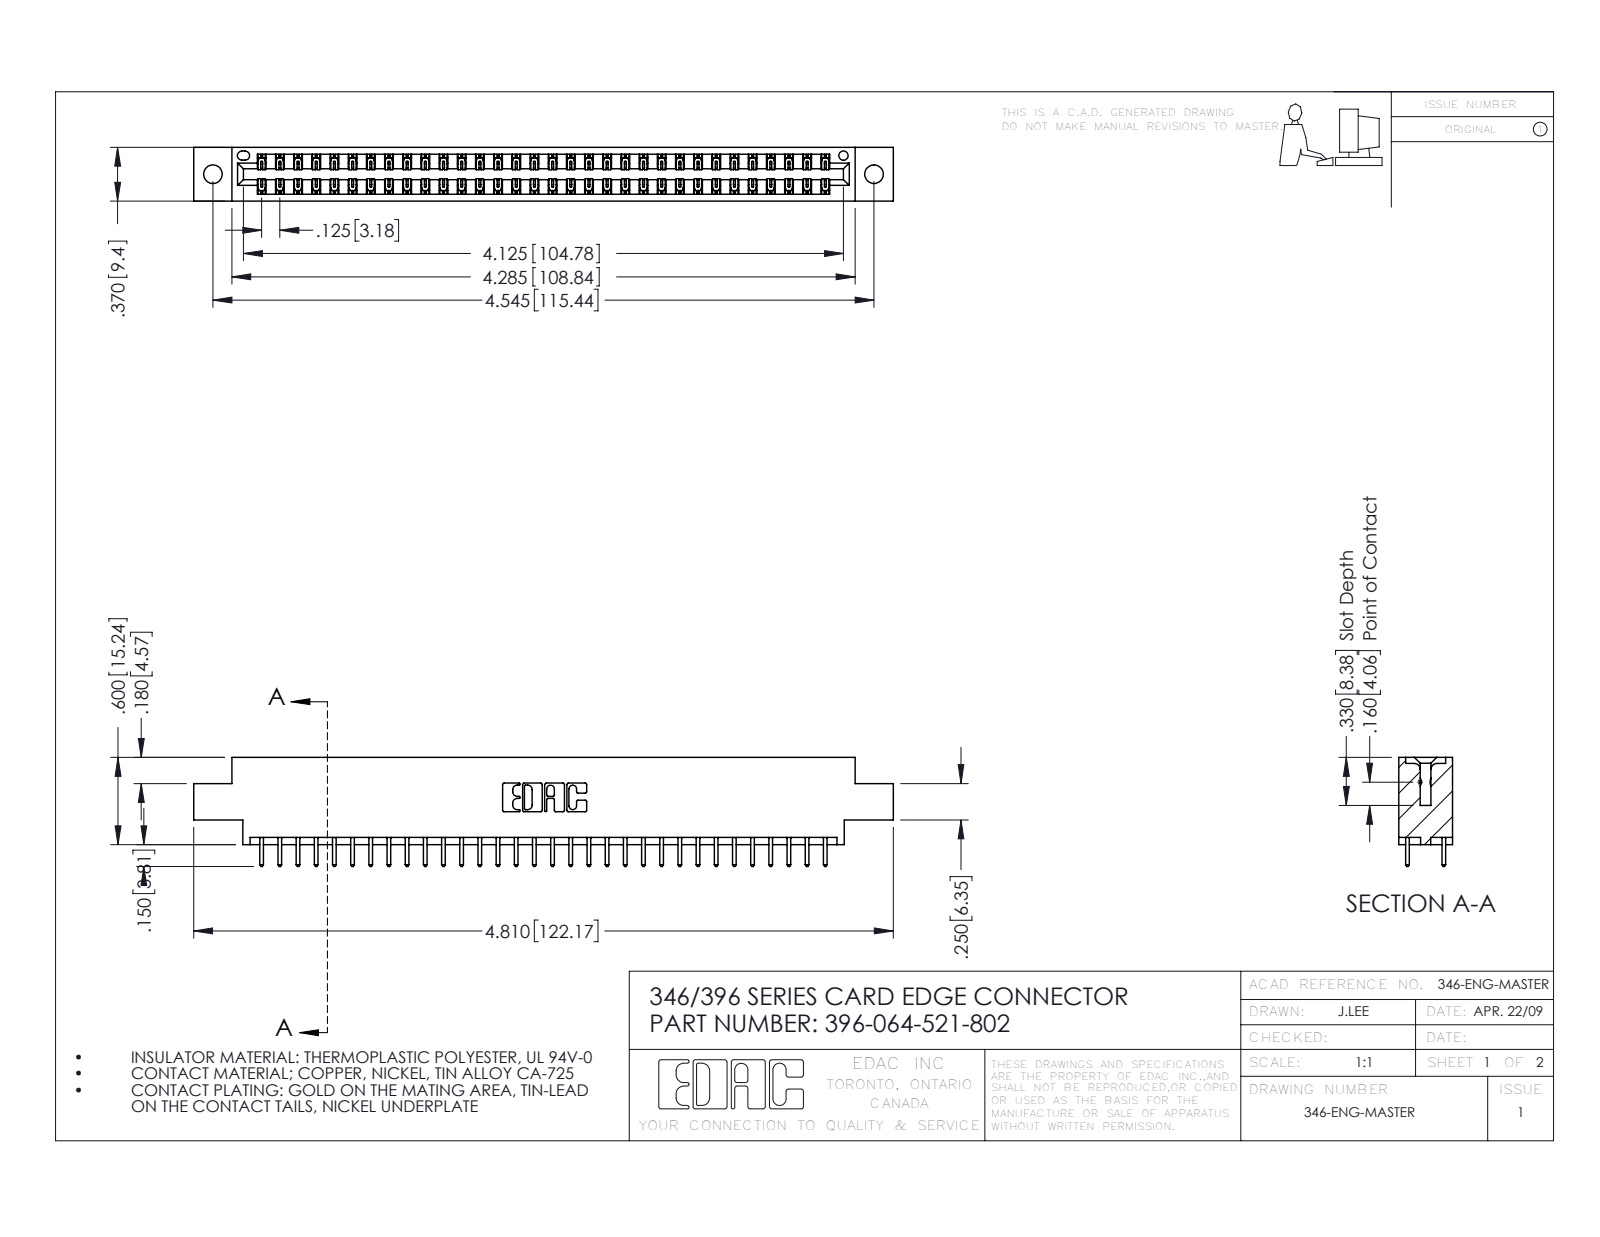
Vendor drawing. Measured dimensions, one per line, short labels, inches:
name: 345-292-001_345-293-121; 396-064-521-802; 346 Part_0.170 Offset - 0.128 Dia
written by: SolidWorks 2016 (CONFIG_CONTROL_DESIGN)
unit: in
bodies: 65 solids, 3454 faces (2320 planar, 1134 cylindrical, 0 other)
size: 4.81 × 0.75 × 0.37
volume: 0.709 in³; area: 24.1 in²
holes: 2× ⌀0.128, 1× ⌀0.064
rounds: 96× R0.006, 64× R0.01, 22× R0.01, 6× R0.007, 6× R0.031, 3× R0.026, 2× R0.014, 2× R0.022
face distances: 0.048, 0.322, 0.37, 0.25, 0.072, 0.298, 0.025, 0.275, 0.148, 0.222
hole spacings: 0.246, 4.337, 4.545
